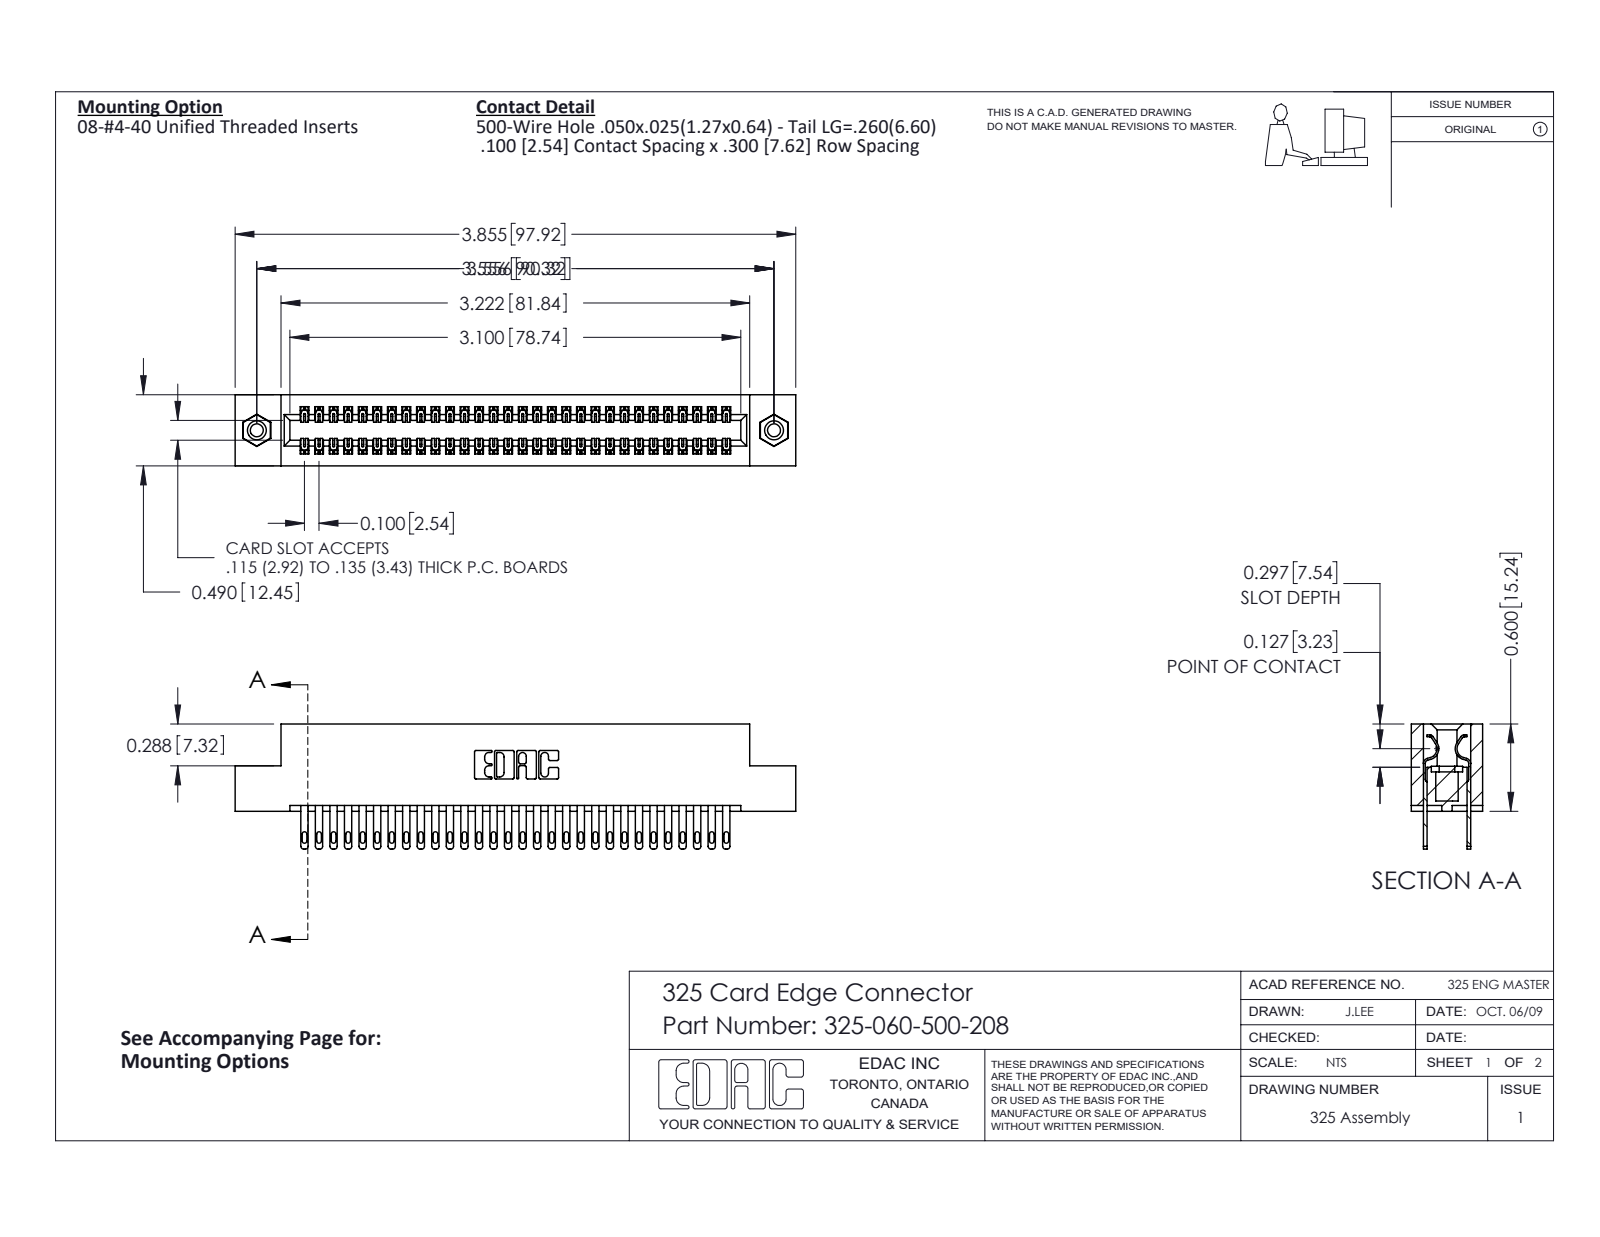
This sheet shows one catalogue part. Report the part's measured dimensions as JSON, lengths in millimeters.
{"part_name": "325 Part_TI; 325-060-500-208; 325-292-001_325-293-100; 345-250-001_345-250-003-102", "step_written_by": "SolidWorks 2016 (CONFIG_CONTROL_DESIGN)", "units": "millimeters", "bodies": {"solids": 63, "faces": 3054, "planar": 1902, "cylindrical": 1136, "other": 16}, "overall_size": [97.9, 21.8, 12.4], "volume_mm3": 12700, "surface_area_mm2": 15740, "round_holes": [[2.3, 2], [3.2, 2], [4.1, 2]], "round_bosses_or_shafts": [[3.9, 2]], "partial_cylinders_radius": [[0.2, 90], [0.4, 60], [0.5, 60], [0.3, 22], [0.2, 6], [0.8, 6], [0.7, 3], [0.4, 2]], "face_to_face_distances": [2.1, 10.3, 7.6, 2.7, 9.7, 0.6, 12.4, 8.3, 7, 1], "hole_center_spacings": [90.3]}
